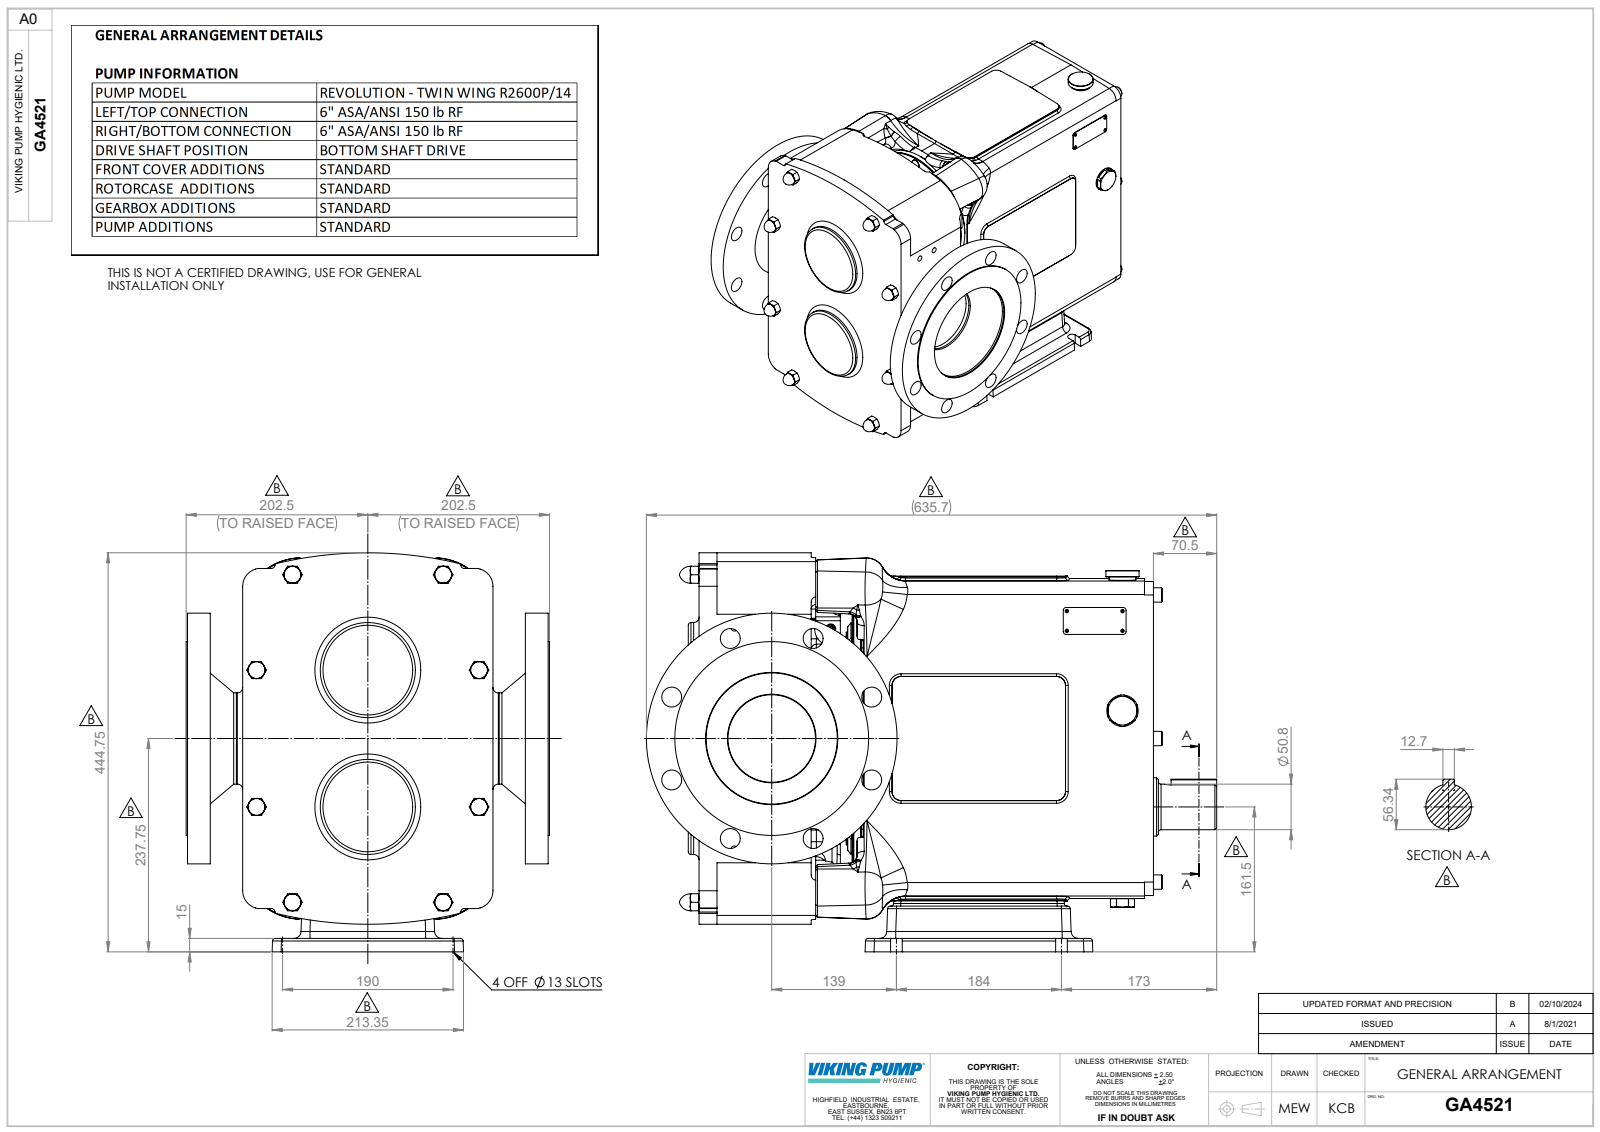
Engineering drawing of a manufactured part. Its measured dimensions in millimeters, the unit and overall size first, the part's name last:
Units: millimetres
Overall size (bounding box): 635.7 × 444.75 × 405
Round holes (diameter × count): ⌀22.2 ×8, ⌀6 ×4, ⌀8.5 ×4, ⌀149 ×2, ⌀35 ×1, ⌀97.55 ×1, ⌀147.4 ×1
Round bosses / shafts (diameter × count): ⌀14 ×10, ⌀8 ×10, ⌀16 ×6, ⌀18 ×4, ⌀187 ×2, ⌀140 ×2, ⌀106 ×2, ⌀85 ×2
Partial cylindrical surfaces — rounded edges, fillets, slot ends (radius × count): R3 ×44, R6 ×44, R10 ×28, R0.2 ×24, R5 ×16, R8 ×10, R15 ×8, R20 ×6
Main face-to-face distances: 80.6, 270.6, 193, 190, 506.5, 349, 41.5, 77.6, 273.6, 3
Hole centre spacings: 120.65, 170.63, 222.94, 92.34, 92.35, 241.31, 13.37, 23.32
Volume: 43 390 000 mm³ · Surface area: 1 477 000 mm²
Bodies: 3 solids, 1608 faces (449 planar, 440 cylindrical, 719 other)
Part name (STEP PRODUCT): Copy of RA94-5301-67^GA4521; GA4521; Copy of R2600 CPP H BSD^GA4521
STEP written by: SolidWorks 2023 (AUTOMOTIVE_DESIGN)
